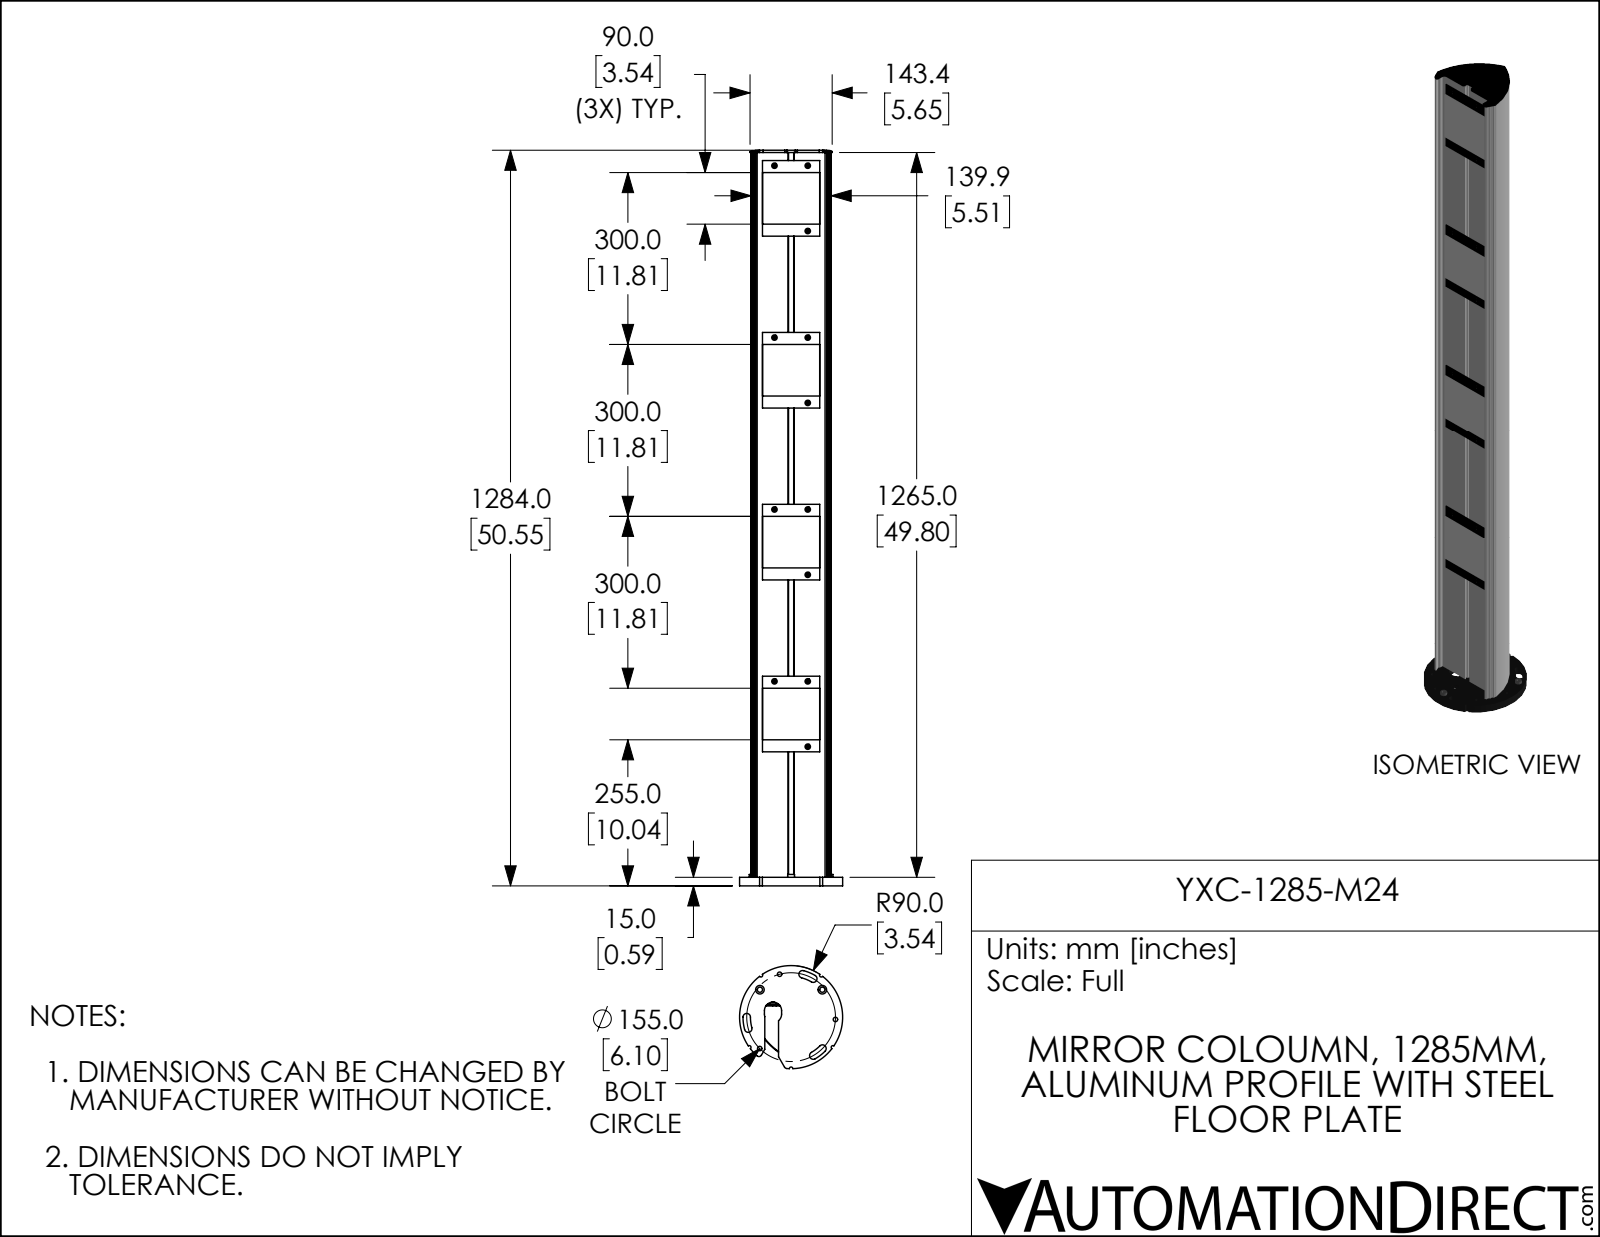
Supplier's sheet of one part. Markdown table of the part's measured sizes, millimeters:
| quantity | value |
| --- | --- |
| part name | YXC_1285_M24 |
| STEP written by | Creo Elements/Direct Modeling 18.1B 29-Sep-2012 (C) Parametric Technology GmbH (AUTOMOTIVE_DESIGN) |
| units | millimeters |
| bodies | 1 solid, 439 faces (285 planar, 116 cylindrical, 38 other) |
| overall size | 1284 × 180 × 179.95 |
| volume | 11 870 000 mm³ |
| surface area | 786 368 mm² |
| round holes (diameter × count) | 7.8 × 3, 15 × 3, 9 × 2, 4.4 × 1 |
| round bosses / shafts (diameter × count) | 6 × 12, 12 × 3, 180 × 1 |
| partial cylindrical surfaces (radius × count) | 3 × 9, 6.5 × 6, 6 × 5, 1.32 × 4, 119 × 4, 5 × 3, 1 × 2, 1.32 × 2 |
| main face-to-face distances | 1.5, 3, 5, 6.5, 15, 3.5, 2, 10, 12, 8.5 |
| hole center spacings | 54.52, 31.88, 31.94, 43.73, 56.78, 79.27, 94.41, 94.46 |
